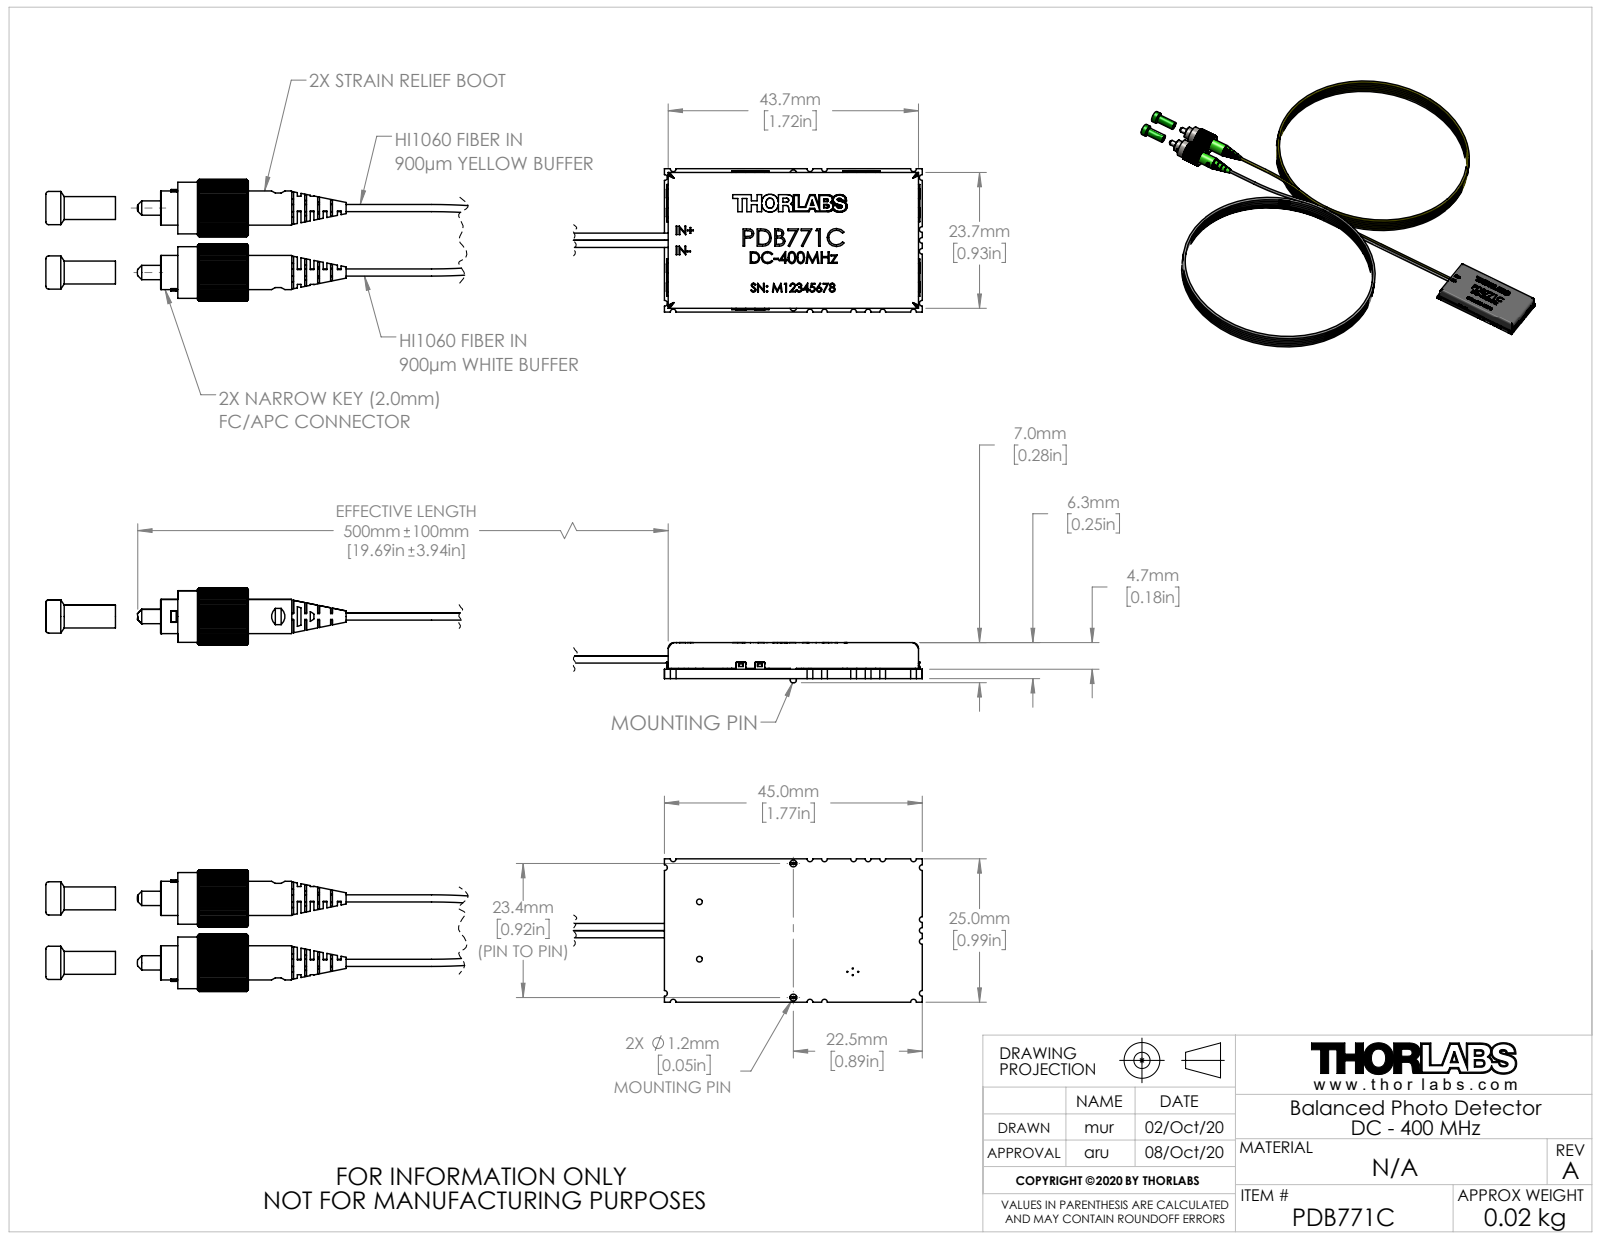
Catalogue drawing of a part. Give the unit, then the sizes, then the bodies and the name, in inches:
Units: inches
Overall size (bounding box): 8.969 × 7.972 × 0.652
Round holes (diameter × count): ⌀0.008 ×4, ⌀0.039 ×2, ⌀0.047 ×2, ⌀0.055 ×2, ⌀0.104 ×2, ⌀0.119 ×2, ⌀0.12 ×2, ⌀0.155 ×2, ⌀0.175 ×2, ⌀0.2 ×2, ⌀0.325 ×2, ⌀0.355 ×2
Round bosses / shafts (diameter × count): ⌀0.049 ×6, ⌀0.01 ×3, ⌀0.28 ×2, ⌀0.235 ×2, ⌀0.228 ×2, ⌀0.195 ×2, ⌀0.157 ×2, ⌀0.15 ×2
Partial cylindrical surfaces — rounded edges, fillets, slot ends (radius × count): R0.006 ×80, R0.012 ×18, R0.02 ×18, R0.011 ×12, R0.015 ×11, R0.006 ×8, R0.016 ×7, R0.028 ×4
Main face-to-face distances: 0.065, 0.248, 0.183, 0.236, 0.171, 0.922, 0.038, 0.933, 0.91, 0.128
Hole centre spacings: 0.044, 0.36, 0.378, 0.698, 0.922, 0.03, 0.045, 0.075
Volume: 0.577 in³ · Surface area: 42.96 in²
Bodies: 35 solids, 3212 faces (2413 planar, 589 cylindrical, 210 other)
Part name (STEP PRODUCT): 20.11.23_PDB771C_WEB
STEP written by: SolidWorks 2018 (AUTOMOTIVE_DESIGN)
